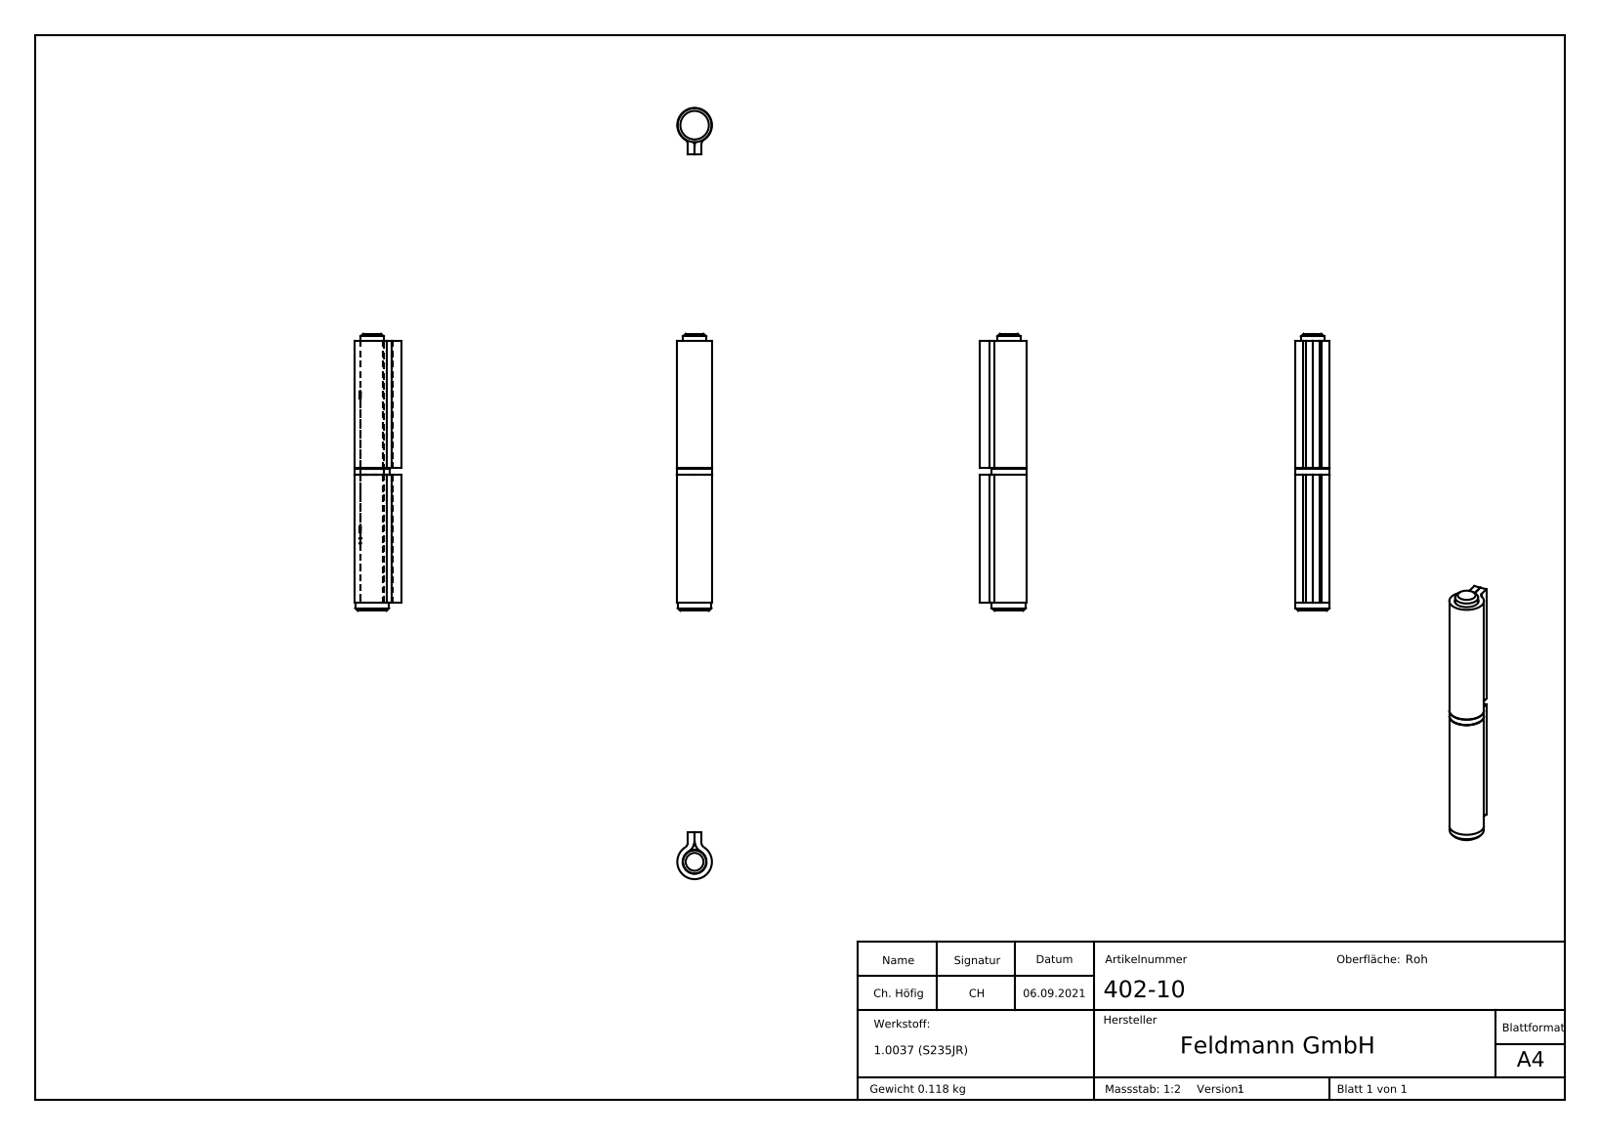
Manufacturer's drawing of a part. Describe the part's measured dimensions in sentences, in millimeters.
The part is named "402-xx Teil1; 402-xx Teil2; 402-xx Teil3; 402-10 (+5 more)". Its 3-D file was written by "SolidWorks 2018 (CONFIG_CONTROL_DESIGN)". It is 4 solids with 304 faces: 148 planar, 38 cylindrical and 118 other. Overall it measures 104 by 17.5 by 13 millimeters. Its volume is 15 119 cubic millimeters and its surface area 12 356 square millimeters. Round holes: 1 of diameter 9. Round bosses or shafts: 1 of diameter 13, 1 of diameter 12.7, 1 of diameter 8.7. Partial cylindrical surfaces (rounded edges, fillets, slot ends): 2 of radius 2, 2 of radius 4.5, 1 of radius 4.6. The main face-to-face distances are 2.5, 2.6, 5.1, 50.5, 48, 3, 51, 53.5, 101.5, 98.5.
